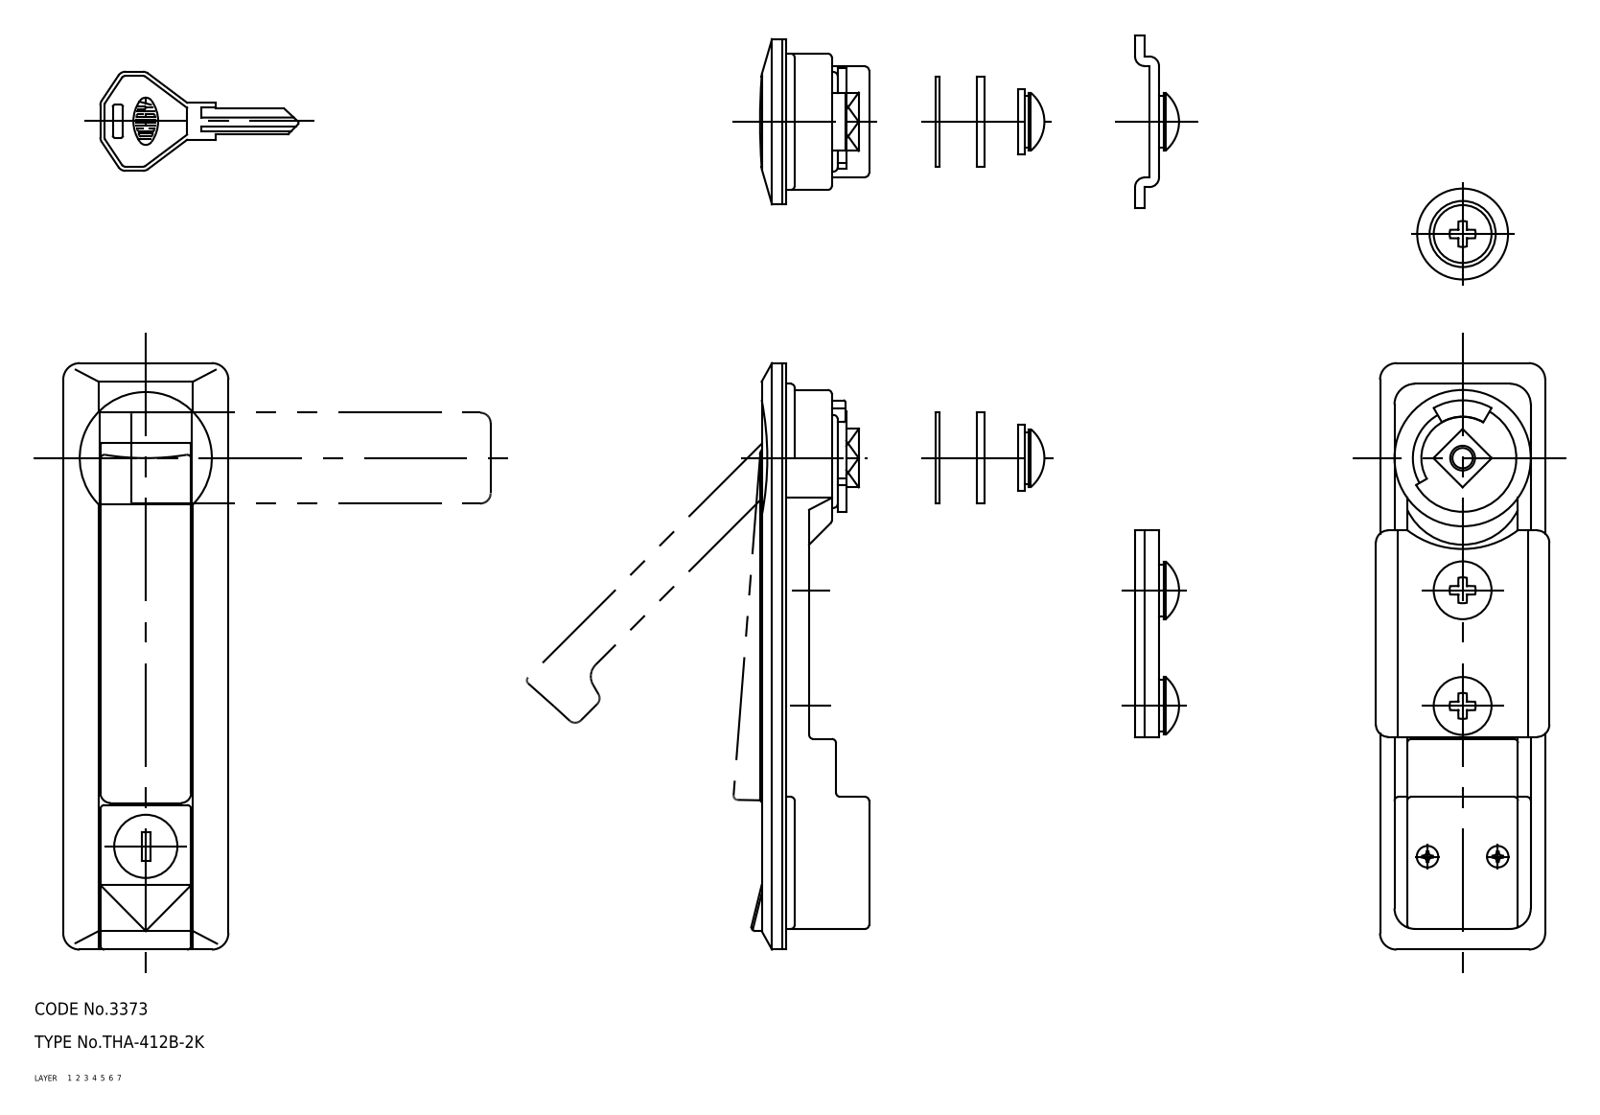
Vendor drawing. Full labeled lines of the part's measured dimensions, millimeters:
Part name (STEP PRODUCT): washer_B; screw_A; screw_B; base (+8 more)
STEP written by: CADfix (AUTOMOTIVE_DESIGN)
Units: millimetres
Bodies: 20 solids, 511 faces (0 planar, 0 cylindrical, 511 other)
Overall size (bounding box): 142 × 107.61 × 42
Volume: 59 216 mm³ · Surface area: 52 135 mm²
